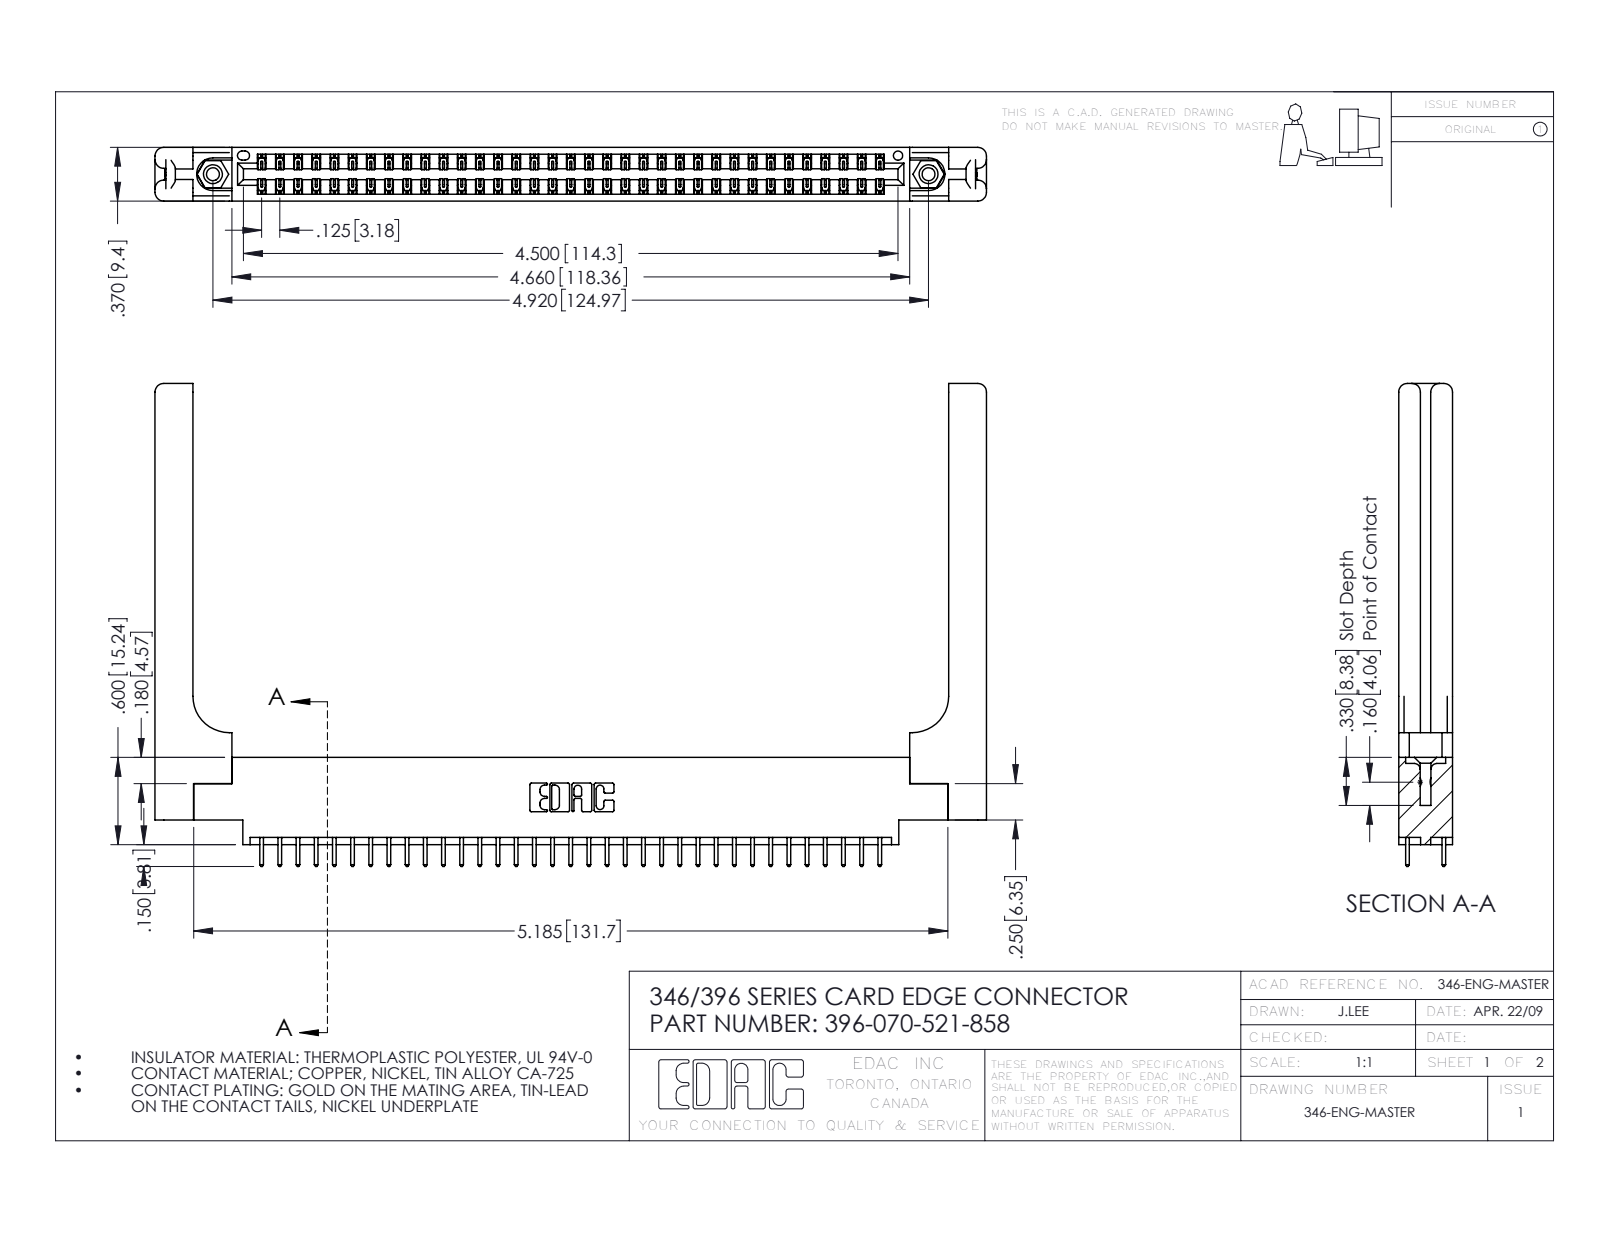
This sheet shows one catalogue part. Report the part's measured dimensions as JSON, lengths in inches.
{"part_name": "345-250-001_345-250-001-102; 346 Part_0.170 Offset - 0.156 Dia-TH; 345-292-001_345-293-121; 346-220-058_345-220-058 (+1 more)", "step_written_by": "SolidWorks 2016 (CONFIG_CONTROL_DESIGN)", "units": "inches", "bodies": {"solids": 75, "faces": 4022, "planar": 2678, "cylindrical": 1284, "other": 60}, "overall_size": [5.716, 3.32, 0.37], "volume_in3": 1.307, "surface_area_in2": 37.18, "round_holes": [[0.089, 2], [0.125, 2], [0.156, 2], [0.064, 1]], "round_bosses_or_shafts": [[0.155, 2]], "partial_cylinders_radius": [[0.006, 105], [0.01, 70], [0.01, 22], [0.06, 16], [0.007, 6], [0.031, 6], [0.026, 3], [0.014, 2]], "face_to_face_distances": [0.37, 0.048, 0.322, 0.072, 0.148, 0.15, 0.25, 0.025, 0.298, 0.275], "hole_center_spacings": [0.246, 4.711, 4.92]}
